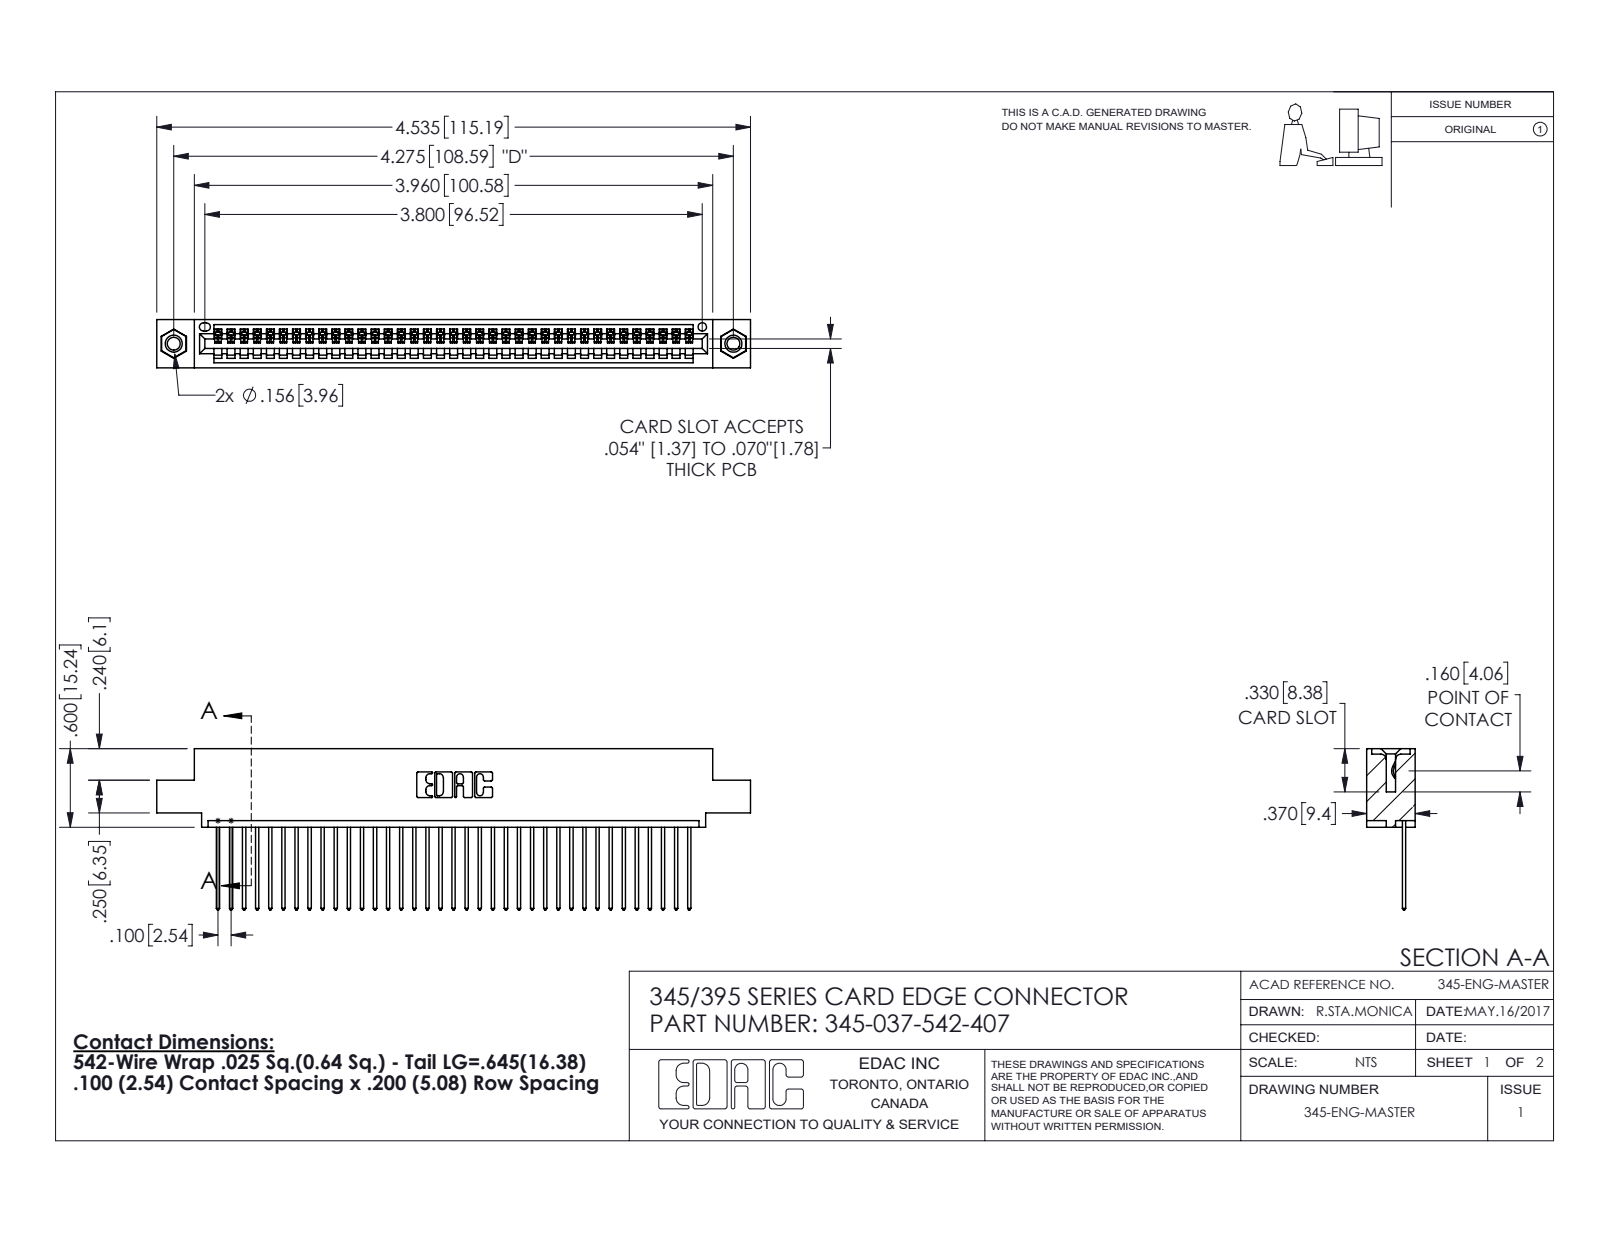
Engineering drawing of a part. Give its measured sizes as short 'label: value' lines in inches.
name: 345-292-001_345-293-142; 345-250-001_345-250-005-103; 345 Part_0.110 Offset - 0.156 Dia-TI; 345-037-542-407
written by: SolidWorks 2016 (CONFIG_CONTROL_DESIGN)
unit: in
bodies: 40 solids, 2336 faces (1596 planar, 724 cylindrical, 16 other)
size: 4.535 × 1.232 × 0.37
volume: 0.665 in³; area: 23.32 in²
holes: 2× ⌀0.098, 2× ⌀0.125, 2× ⌀0.156, 1× ⌀0.064
bosses: 2× ⌀0.155
rounds: 74× R0.006, 74× R0.01, 22× R0.01, 6× R0.007, 6× R0.031, 3× R0.026, 2× R0.031, 2× R0.04
face distances: 0.072, 0.298, 0.37, 0.098, 0.272, 0.025, 0.2, 0.225, 0.149, 0.072
hole spacings: 0.27, 4.039, 4.275
